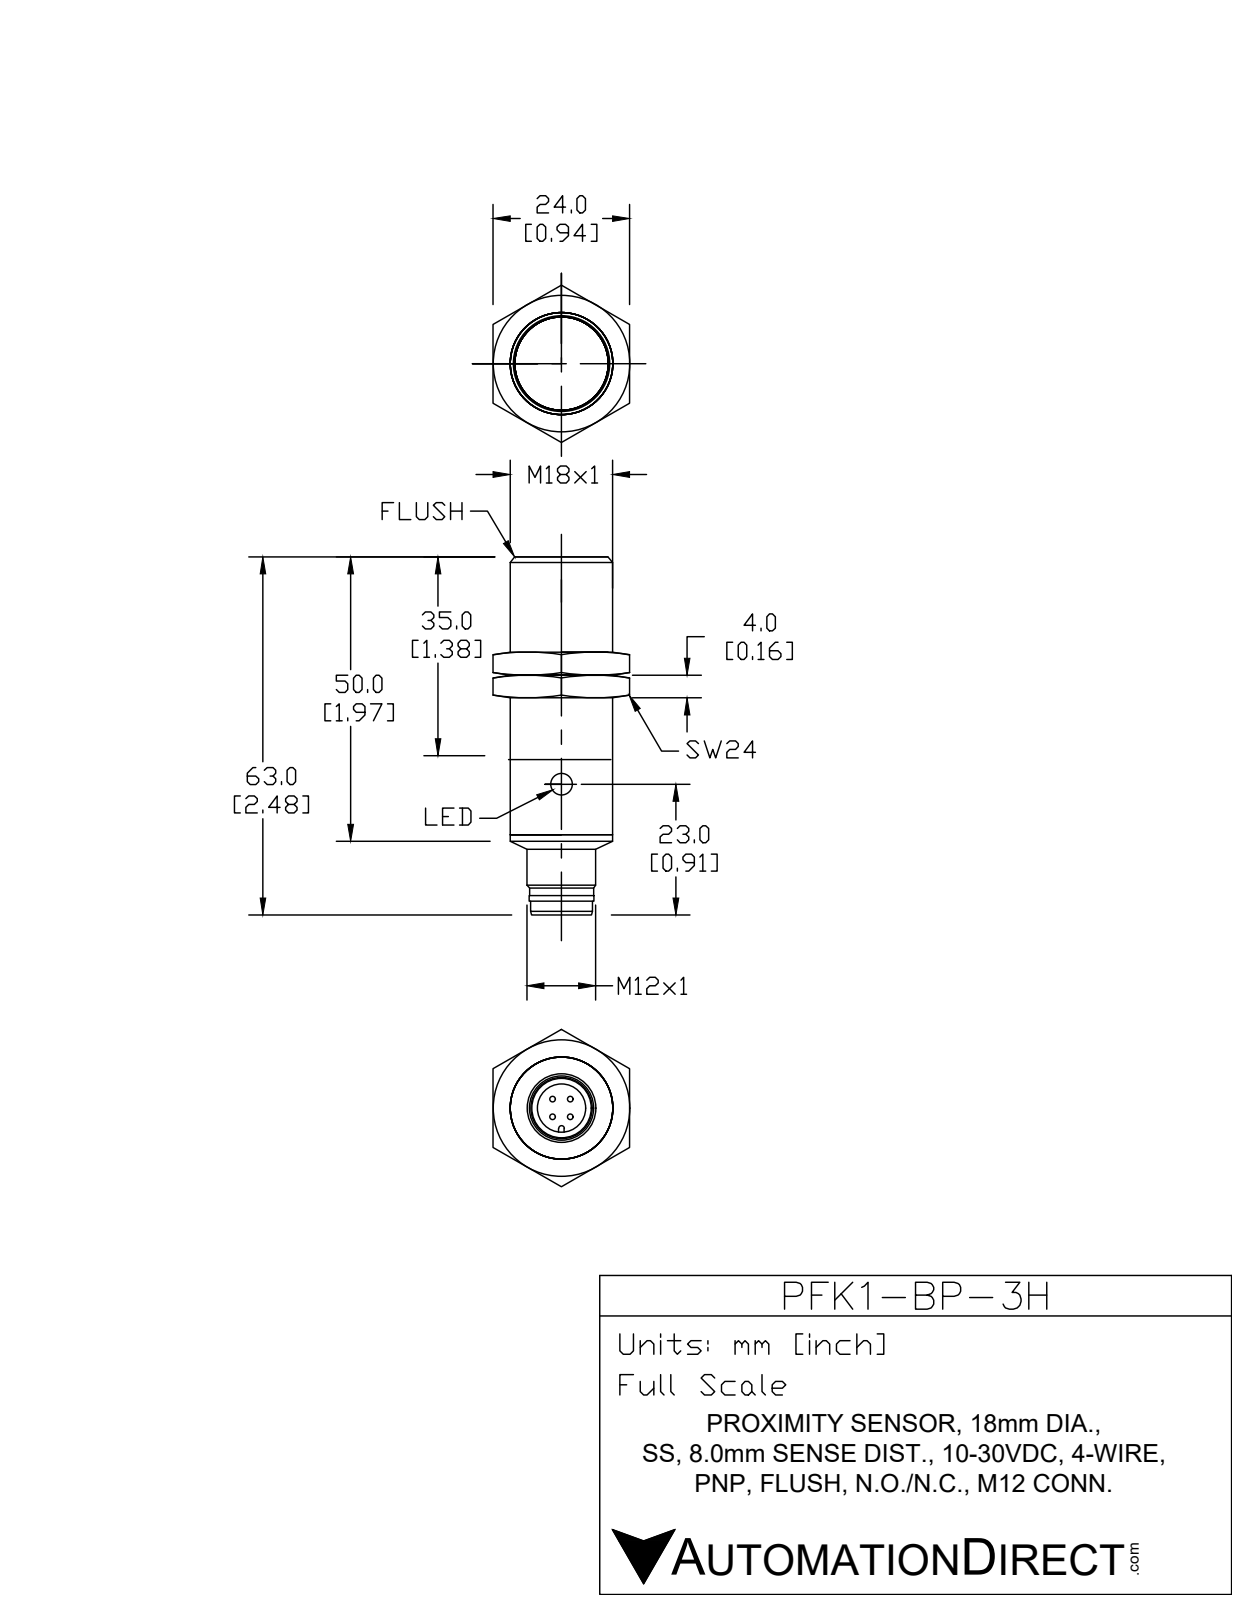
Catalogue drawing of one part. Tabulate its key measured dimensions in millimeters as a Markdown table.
| quantity | value |
| --- | --- |
| part name | PFK1-BP-3H |
| STEP written by | SolidWorks 2017 (AUTOMOTIVE_DESIGN) |
| units | millimeters |
| bodies | 4 solids, 69 faces (12 planar, 35 cylindrical, 22 other) |
| overall size | 63.1 × 18 × 18 |
| volume | 13 700 mm³ |
| surface area | 6 632 mm² |
| round holes (diameter × count) | 4 × 1, 8.4 × 1, 8.5 × 1, 9.5 × 1, 15.8 × 1 |
| round bosses / shafts (diameter × count) | 1 × 4, 18 × 1, 12 × 1, 10.5 × 1, 9.4 × 1 |
| partial cylindrical surfaces (radius × count) | 0.6 × 1, 8.3 × 1 |
| main face-to-face distances | 39.1, 10, 49.1, 53, 43, 3.9, 54.2, 44.2, 5.1, 1.2 |
